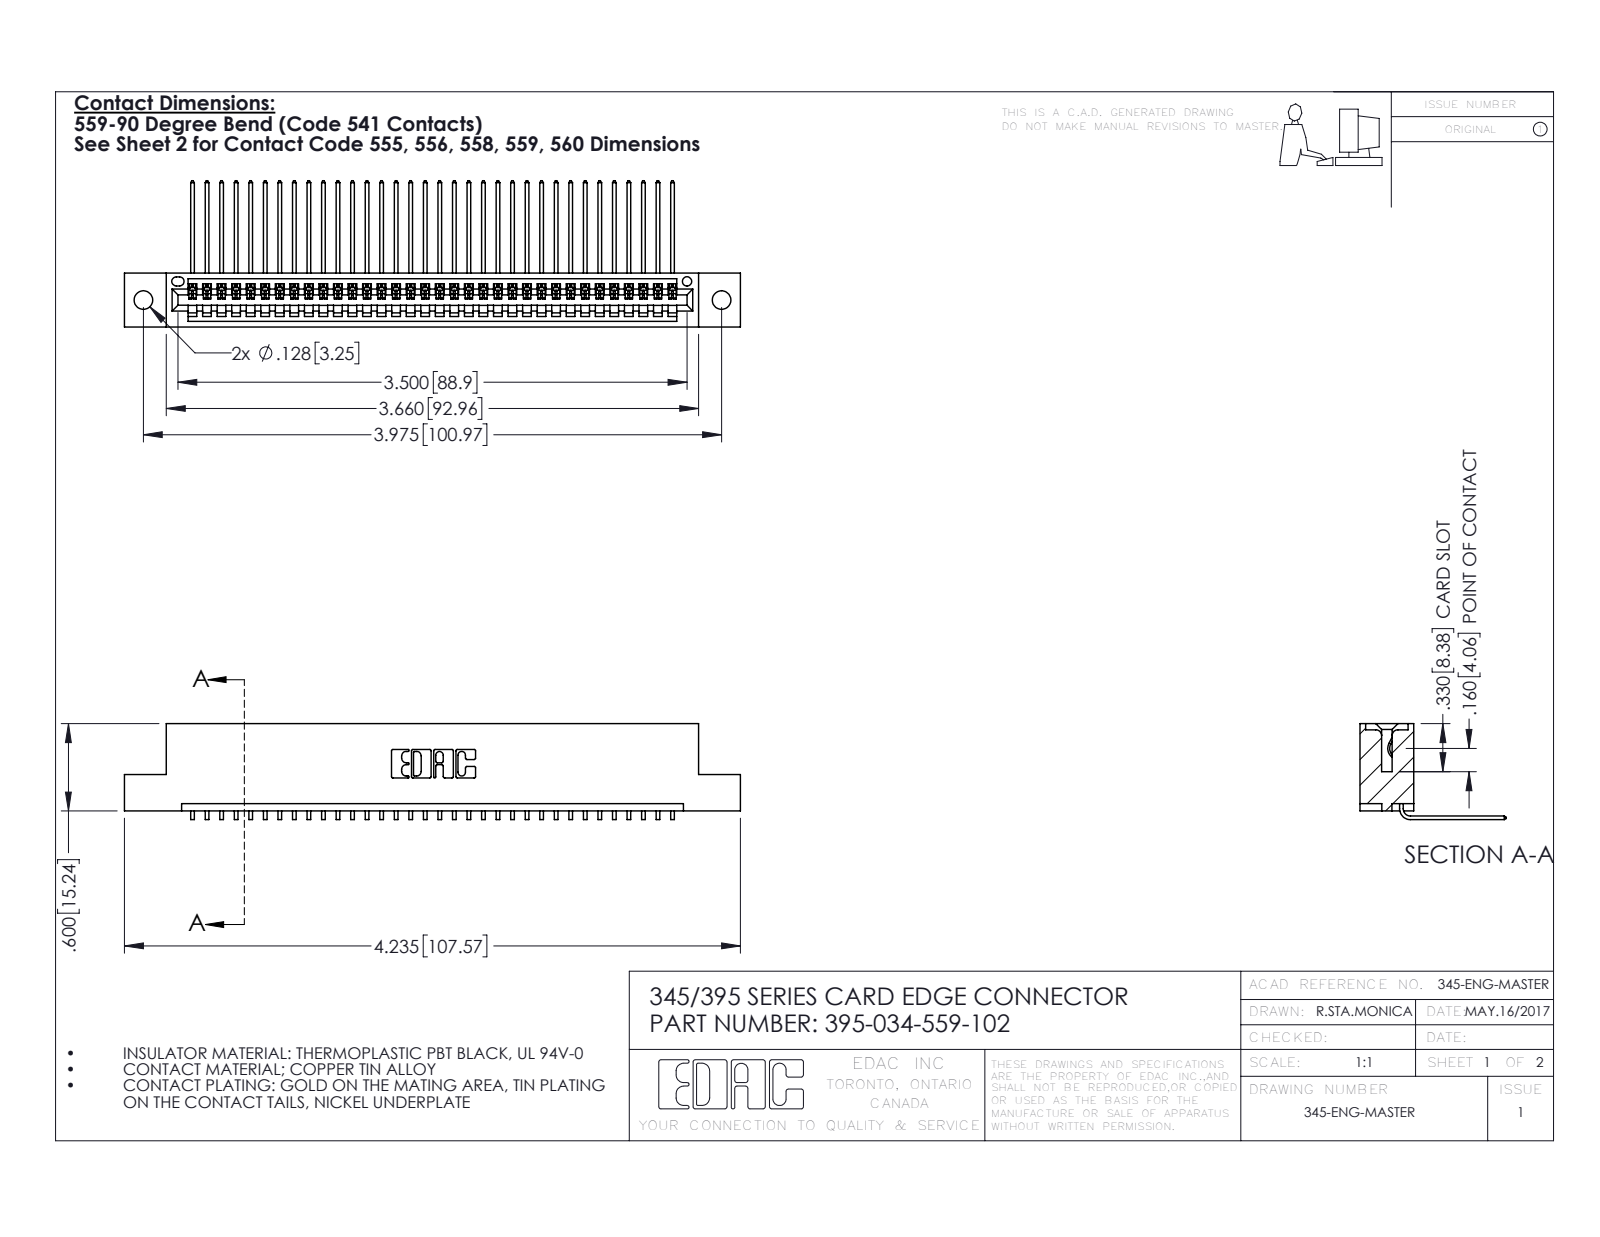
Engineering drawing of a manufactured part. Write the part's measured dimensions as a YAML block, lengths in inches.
part_name: "395-034-559-102; 345-292-001_558 559 Tail - 1; 345 Part_Flush Mounting Lugs - 0.128 Dia"
step_written_by: "SolidWorks 2016 (CONFIG_CONTROL_DESIGN)"
units: inches
bodies: {solids: 35, faces: 2166, planar: 1508, cylindrical: 658, other: 0}
overall_size: [4.235, 1.005, 0.659]
volume: 0.624
surface_area: 21.51
round_holes:
  - {diameter: 0.128, count: 2}
  - {diameter: 0.064, count: 1}
partial_cylinders:
  - {radius: 0.006, count: 68}
  - {radius: 0.01, count: 22}
  - {radius: 0.007, count: 6}
  - {radius: 0.031, count: 6}
  - {radius: 0.026, count: 3}
  - {radius: 0.031, count: 2}
  - {radius: 0.04, count: 2}
  - {radius: 0.014, count: 1}
face_to_face_distances: [0.298, 0.072, 0.37, 0.2, 0.098, 0.272, 0.025, 0.225, 0.149, 0.072]
hole_center_spacings: [0.27, 3.74, 3.975]
